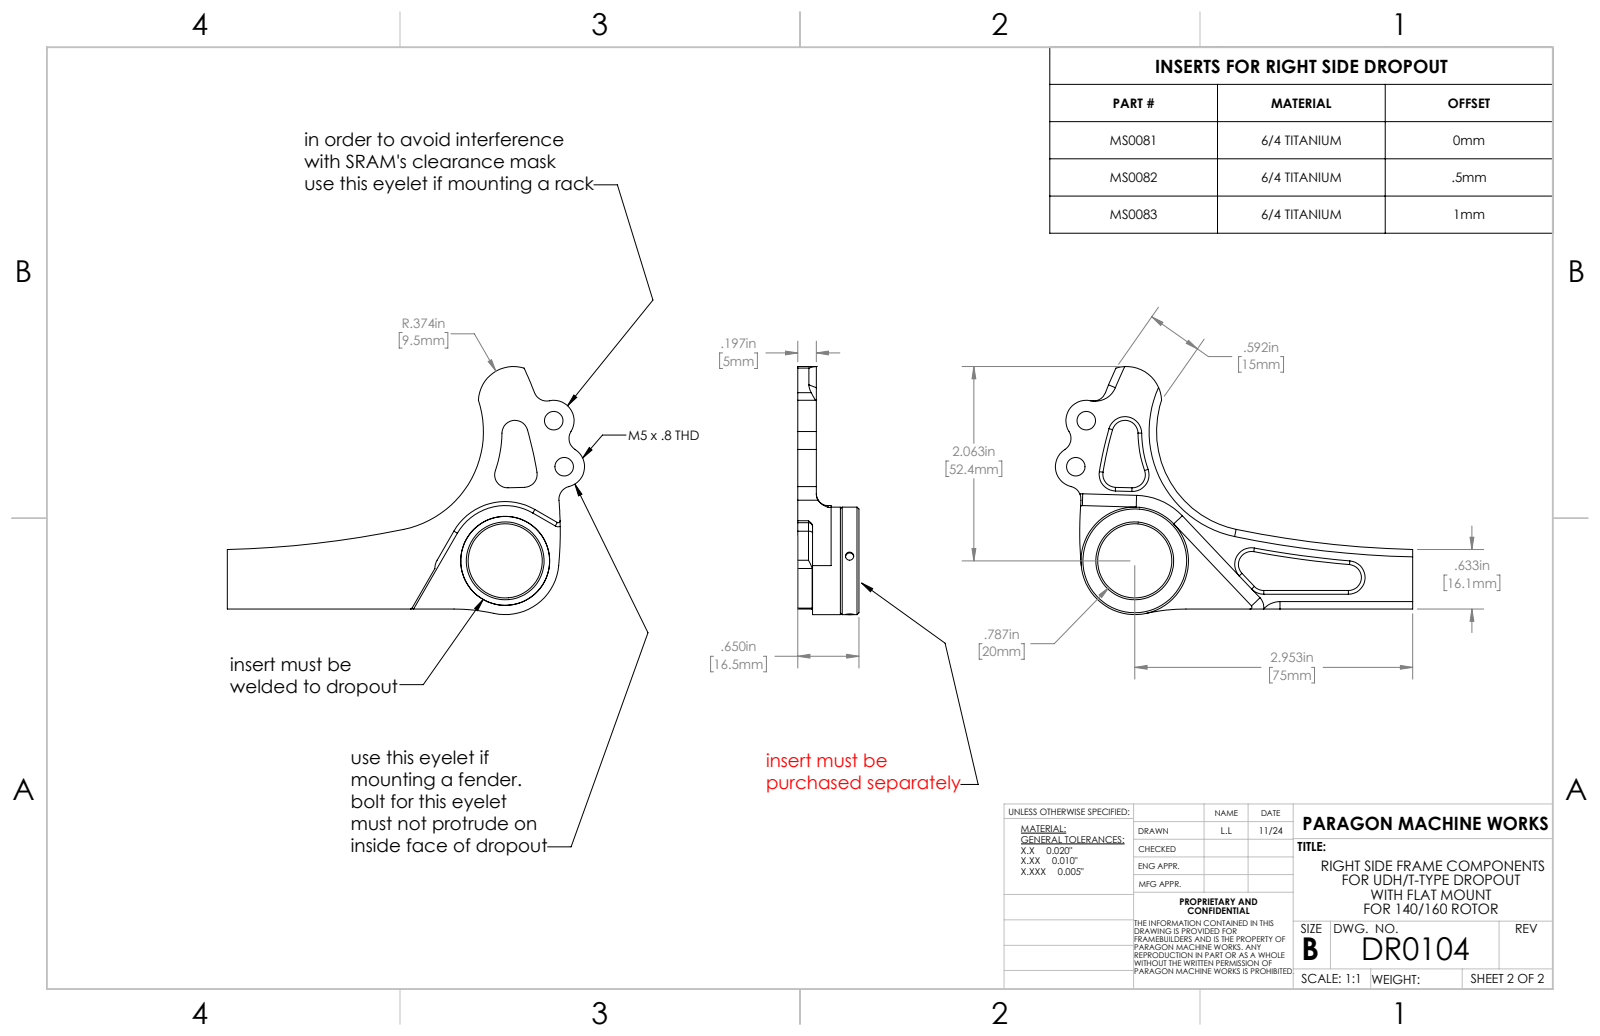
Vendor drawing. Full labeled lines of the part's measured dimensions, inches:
Part name (STEP PRODUCT): DR0104R
STEP written by: SolidWorks 2023 (AUTOMOTIVE_DESIGN)
Units: inches
Bodies: 1 solid, 86 faces (21 planar, 43 cylindrical, 22 other)
Overall size (bounding box): 3.796 × 2.634 × 0.453
Volume: 0.661 in³ · Surface area: 11.32 in²
Round holes (diameter × count): ⌀0.197 ×2, ⌀0.945 ×1
Round bosses / shafts (diameter × count): ⌀1.142 ×1
Partial cylindrical surfaces — rounded edges, fillets, slot ends (radius × count): R0.138 ×9, R0.02 ×4, R0.043 ×2, R0.125 ×2, R0.217 ×2, R0.177 ×1, R0.374 ×1, R0.63 ×1
Main face-to-face distances: 0.197, 0.039, 0.157, 0.118, 0.079, 0.354, 0.236, 0.453, 0.335, 0.295
Hole centre spacings: 0.502, 1.18, 1.575
